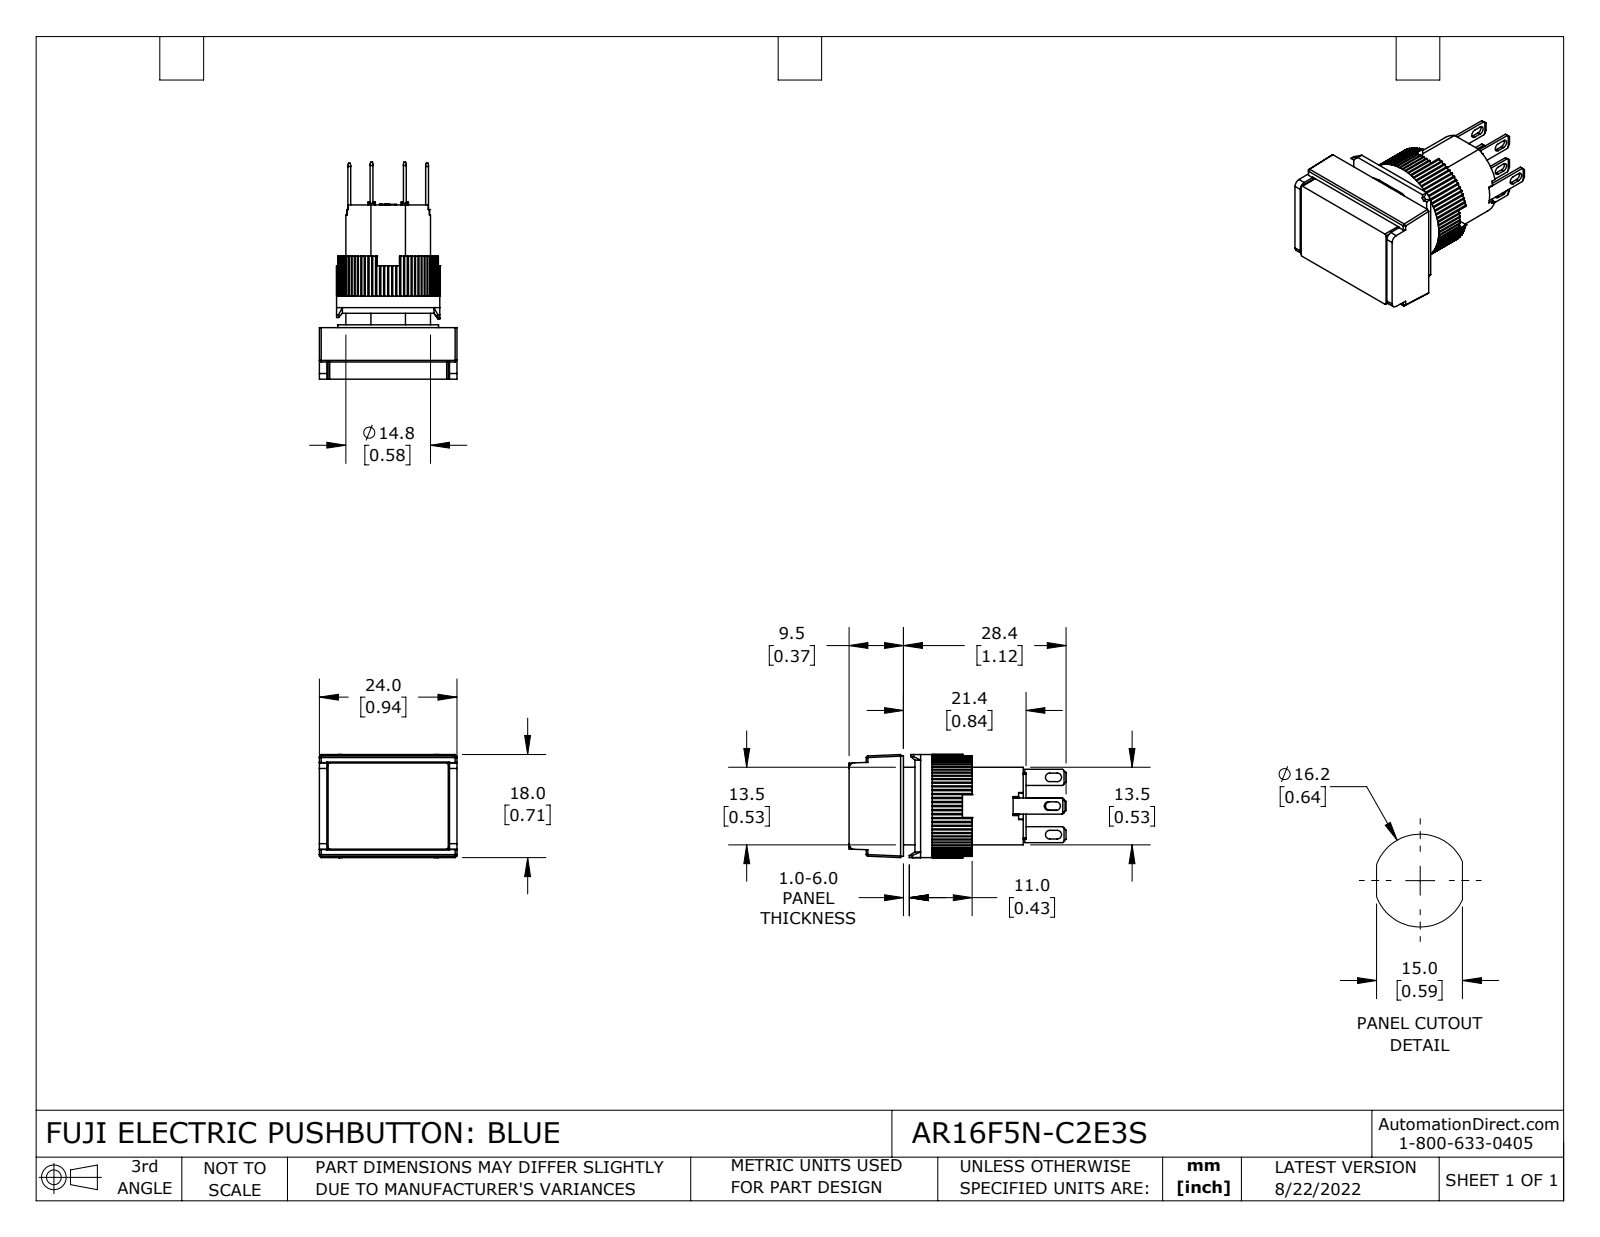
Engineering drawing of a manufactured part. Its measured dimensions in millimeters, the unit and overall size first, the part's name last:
Units: millimetres
Overall size (bounding box): 37.9 × 24 × 18
Round holes (diameter × count): ⌀13.8 ×1, ⌀14.8 ×1
Round bosses / shafts (diameter × count): ⌀18 ×1, ⌀17.6 ×1
Partial cylindrical surfaces — rounded edges, fillets, slot ends (radius × count): R0.3 ×80, R0.2 ×12, R0.8 ×8, R0.3 ×6, R1 ×2
Main face-to-face distances: 5.4, 9, 3.6, 8.9, 12.5, 3.5, 0.5, 21.4, 1.5, 11.5
Volume: 7 280 mm³ · Surface area: 6 004 mm²
Bodies: 14 solids, 843 faces (656 planar, 183 cylindrical, 4 other)
Part name (STEP PRODUCT): AR16F5N-C2E3S
STEP written by: SolidWorks 2021 (CONFIG_CONTROL_DESIGN)
